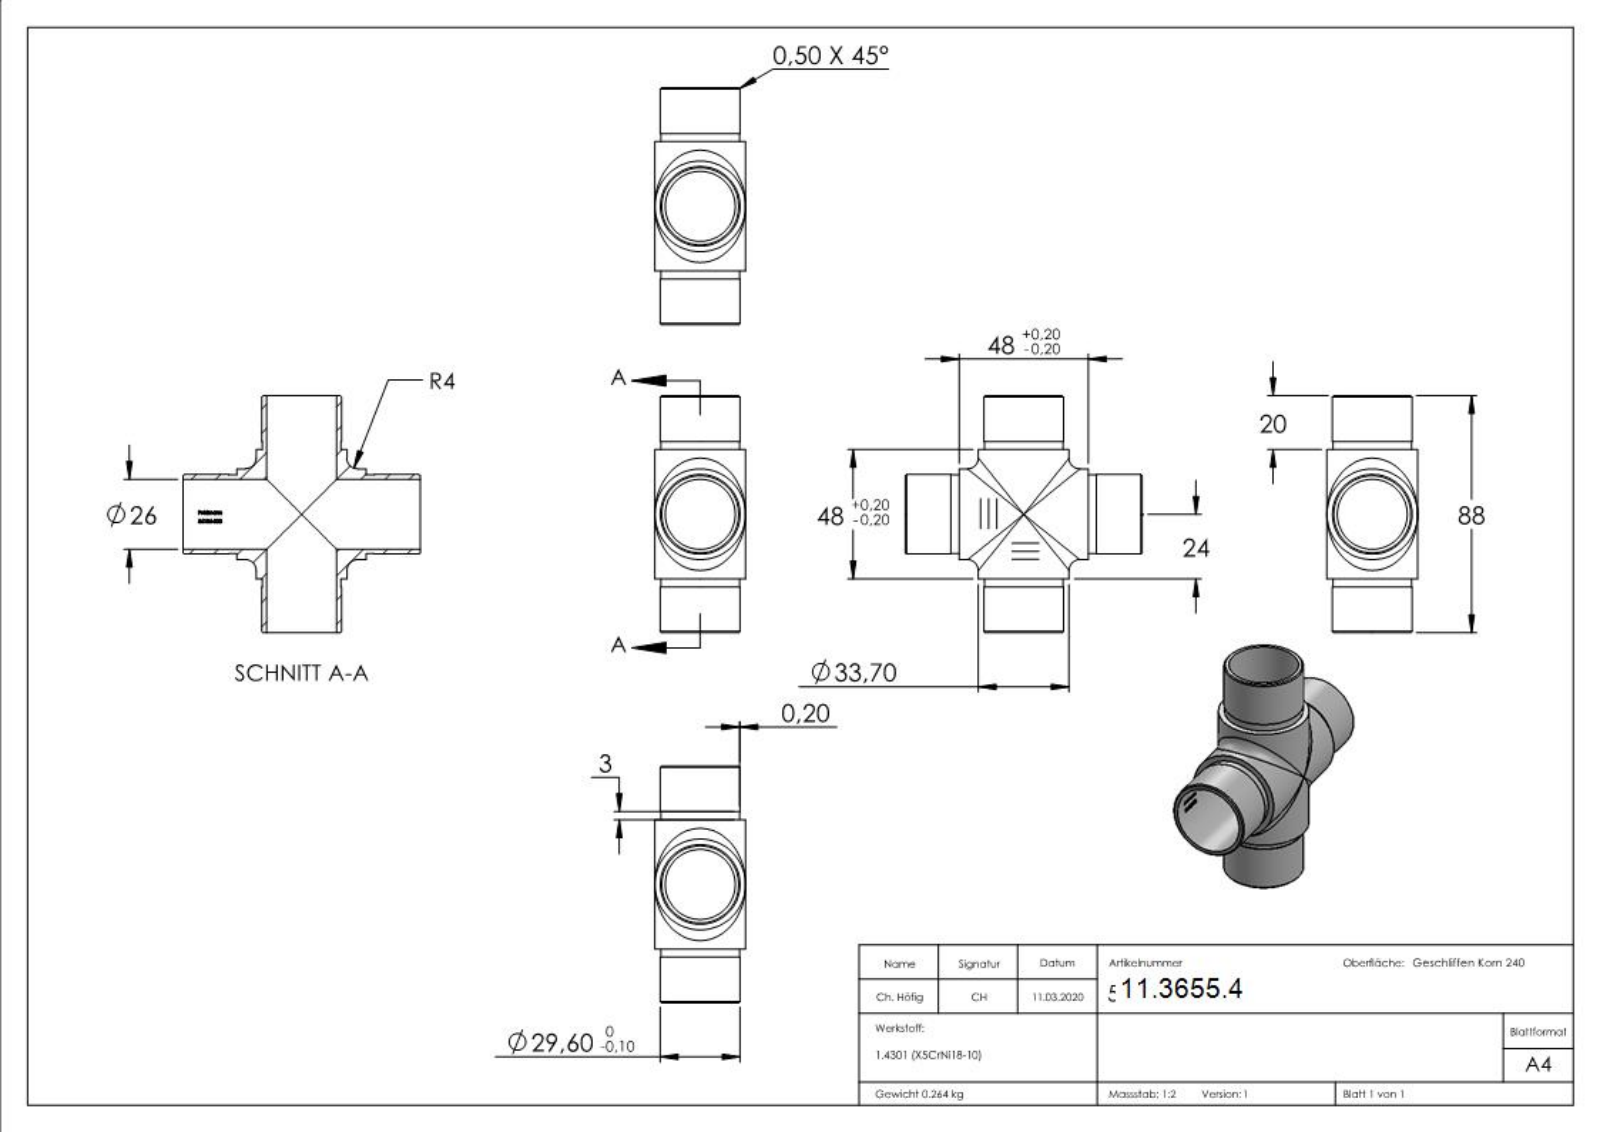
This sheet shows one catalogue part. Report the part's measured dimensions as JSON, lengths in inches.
{"part_name": "56186-320", "step_written_by": "SolidWorks 2015 (CONFIG_CONTROL_DESIGN)", "units": "inches", "bodies": {"solids": 1, "faces": 266, "planar": 97, "cylindrical": 41, "other": 128}, "overall_size": [3.465, 3.465, 1.327], "volume_in3": 2.042, "surface_area_in2": 40.43, "round_holes": [[1.024, 2]], "round_bosses_or_shafts": [[1.327, 2], [1.165, 2], [1.15, 2]], "partial_cylinders_radius": [[0.516, 1]], "face_to_face_distances": [0.787, 2.677, 1.89, 3.465, 0.669, 2.795, 0.118, 2.008, 2.126, 0.015]}
